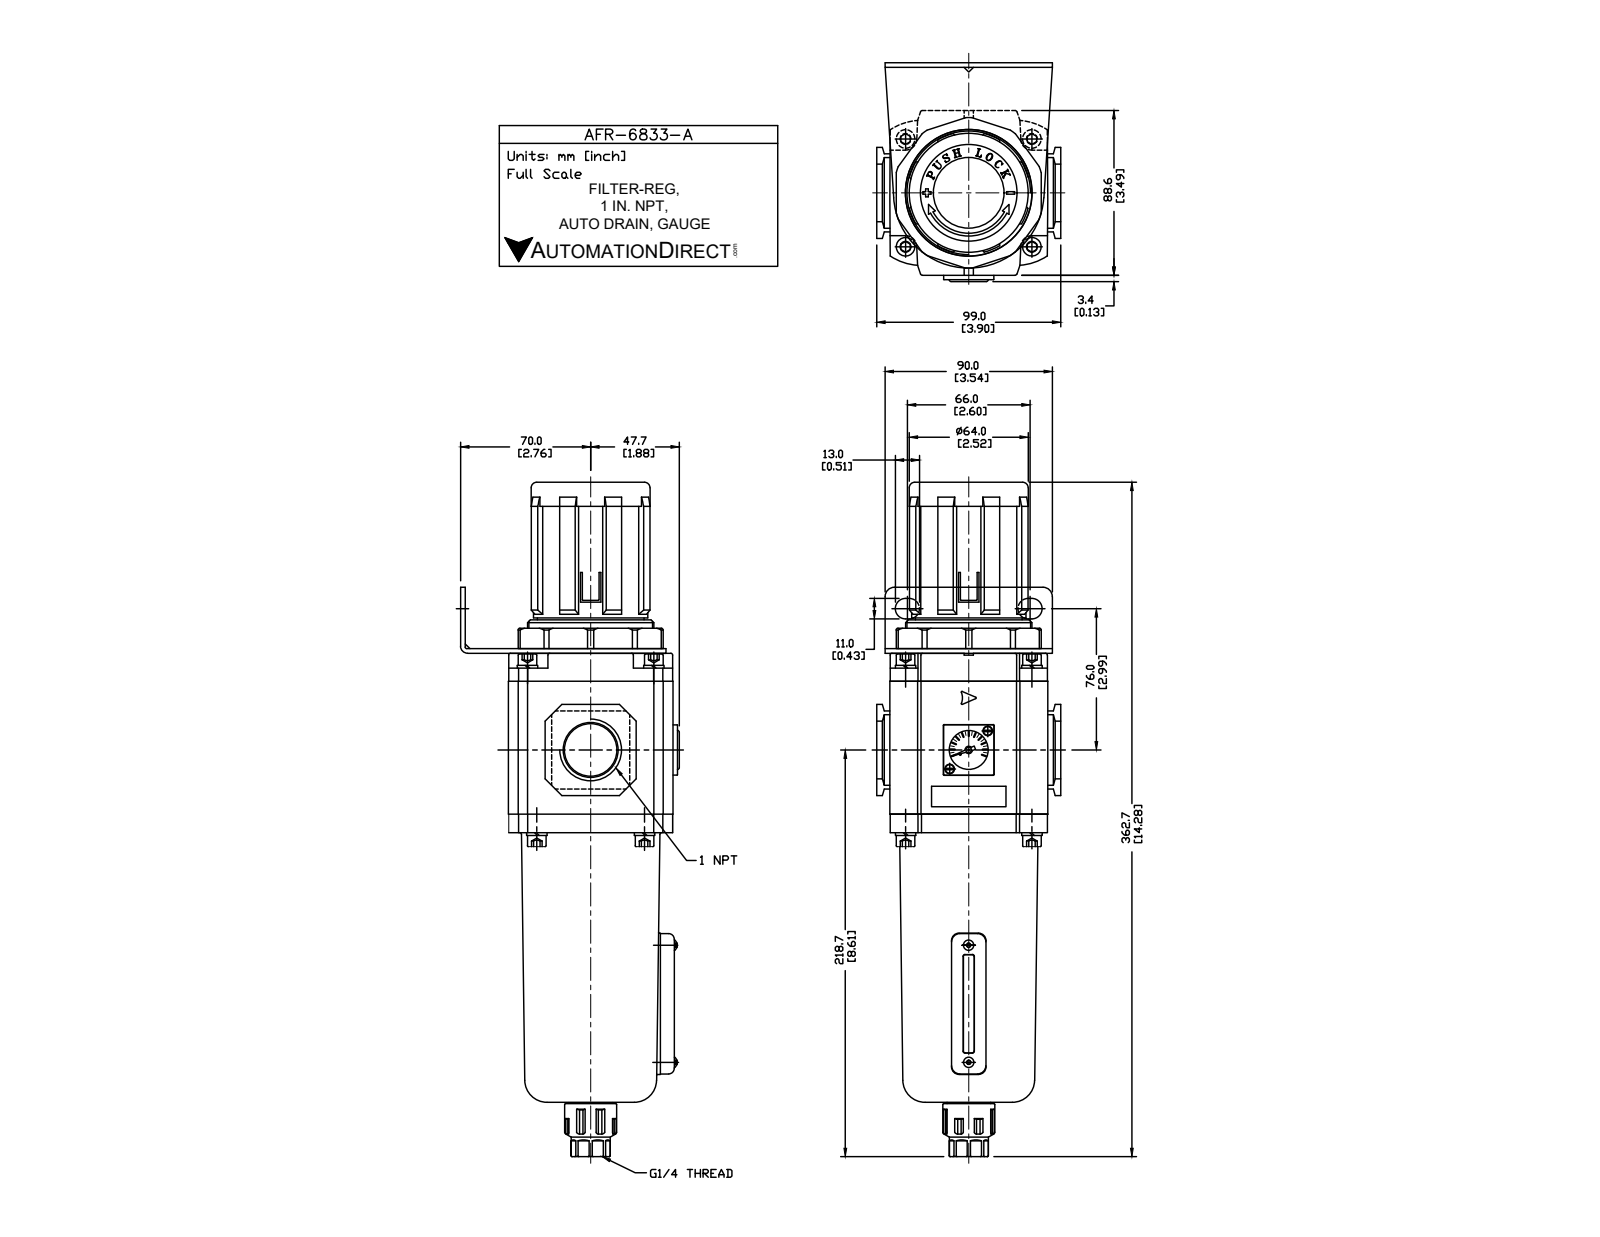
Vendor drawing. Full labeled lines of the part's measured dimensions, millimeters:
Part name (STEP PRODUCT): AFR-6833-A
STEP written by: SolidWorks 2015 (CONFIG_CONTROL_DESIGN)
Units: millimetres
Bodies: 16 solids, 703 faces (439 planar, 175 cylindrical, 89 other)
Overall size (bounding box): 362.7 × 117 × 99
Volume: 1 664 000 mm³ · Surface area: 186 514 mm²
Round holes (diameter × count): ⌀3 ×6, ⌀2 ×1, ⌀12 ×1, ⌀28.98 ×1, ⌀30 ×1, ⌀38 ×1
Round bosses / shafts (diameter × count): ⌀10 ×8, ⌀5.5 ×2, ⌀2.7 ×2, ⌀68 ×1, ⌀64 ×1, ⌀62 ×1, ⌀53.76 ×1, ⌀28 ×1
Partial cylindrical surfaces — rounded edges, fillets, slot ends (radius × count): R1 ×12, R1.2 ×10, R1.3 ×8, R2.5 ×8, R9.5 ×8, R19.9 ×8, R0.5 ×6, R0.3 ×4
Main face-to-face distances: 2.5, 91.2, 88.7, 87.6, 1, 88.6, 85, 92, 10, 3.5
Hole centre spacings: 41.35, 34.68, 53.16, 63.36, 82.71, 69.35
